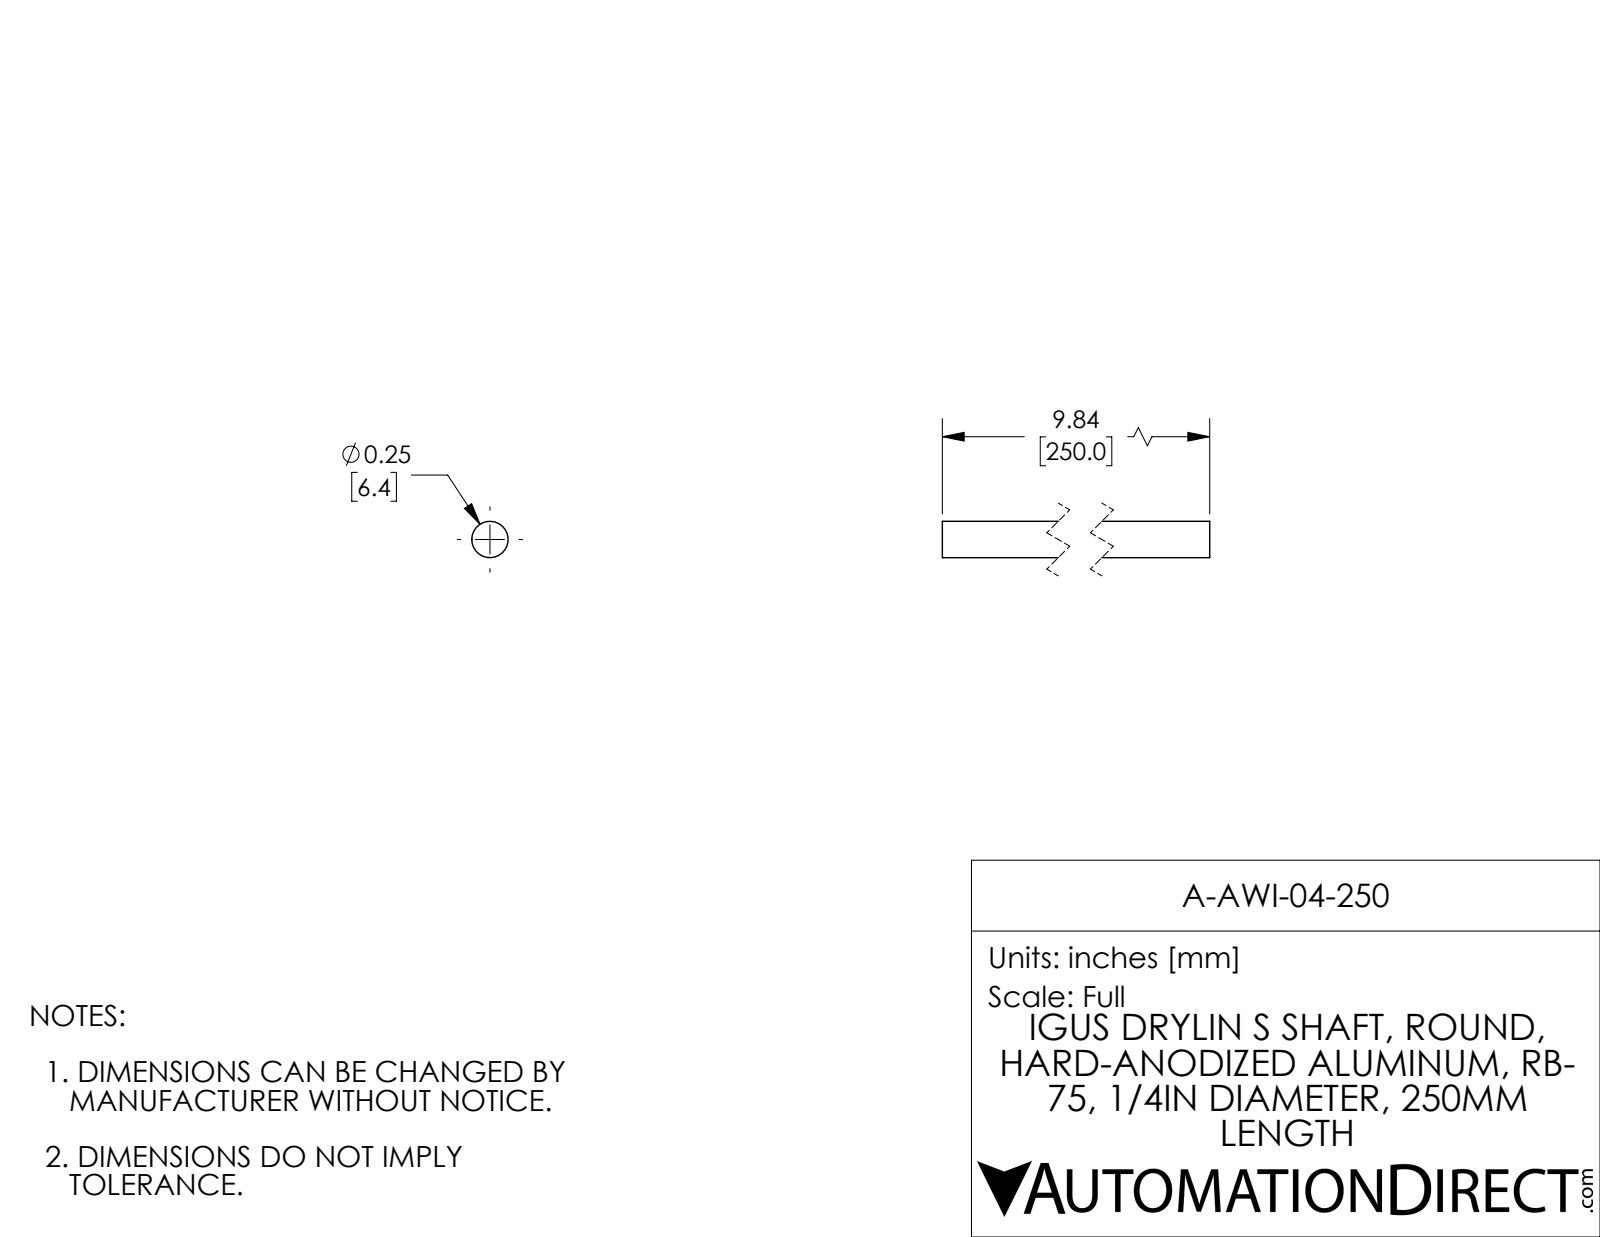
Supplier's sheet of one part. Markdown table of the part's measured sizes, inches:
| quantity | value |
| --- | --- |
| part name | A-AWI-04-250 |
| STEP written by | SolidWorks 2017 (AUTOMOTIVE_DESIGN) |
| units | inches |
| bodies | 1 solid, 4 faces (2 planar, 2 cylindrical, 0 other) |
| overall size | 9.843 × 0.25 × 0.25 |
| volume | 0.483 in³ |
| surface area | 7.828 in² |
| round bosses / shafts (diameter × count) | 0.25 × 1 |
| main face-to-face distances | 9.843 |
